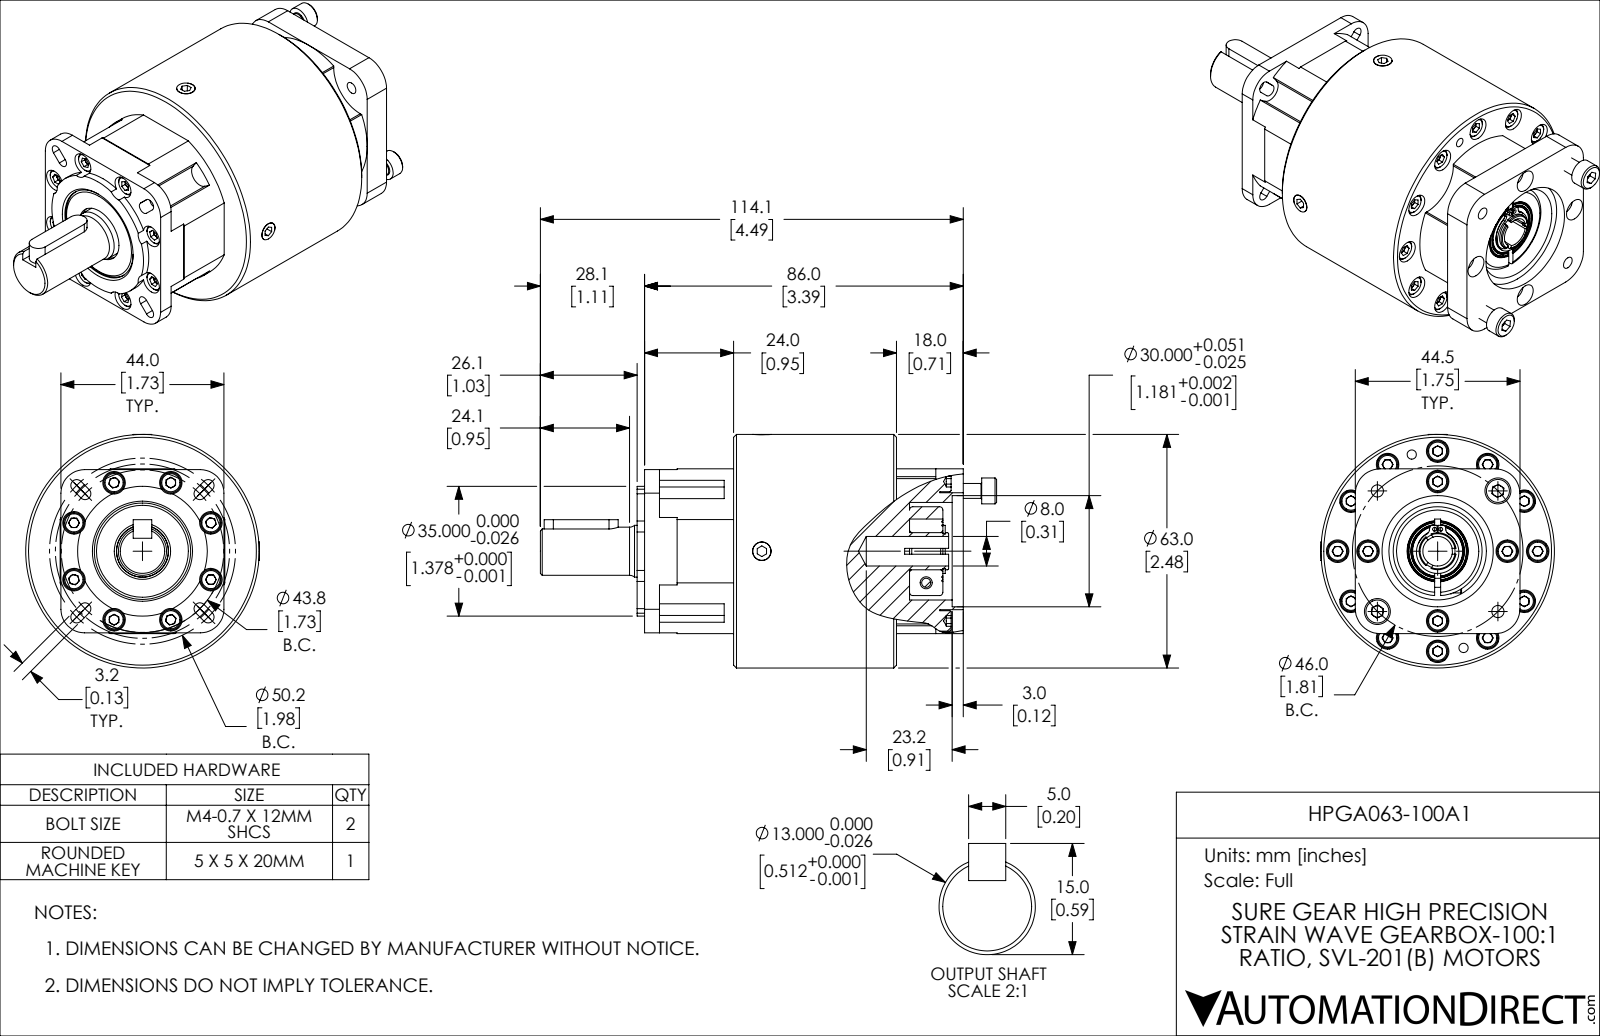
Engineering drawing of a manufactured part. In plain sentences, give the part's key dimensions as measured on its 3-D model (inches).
The part is named "HPGA063-100A1". Its 3-D file was written by "SolidWorks 2021 (CONFIG_CONTROL_DESIGN)". It is 8 solids with 1004 faces: 537 planar, 291 cylindrical and 176 other. Overall it measures 4.847 by 2.48 by 2.48 inches. Its volume is 12.42 cubic inches and its surface area 52.39 square inches. Round holes: 24 of diameter 0.239, 4 of diameter 0.13, 2 of diameter 0.041, 2 of diameter 0.098, 2 of diameter 0.197, 1 of diameter 0.101, 1 of diameter 0.129, 1 of diameter 0.201, 1 of diameter 0.234, 1 of diameter 0.315, 1 of diameter 0.598, 1 of diameter 1.024. Round bosses or shafts: 25 of diameter 0.217, 2 of diameter 0.276, 2 of diameter 0.196, 2 of diameter 0.157, 1 of diameter 2.48, 1 of diameter 0.945, 1 of diameter 0.551, 1 of diameter 0.512. Partial cylindrical surfaces (rounded edges, fillets, slot ends): 8 of radius 0.063, 4 of radius 0.125, 4 of radius 0.25, 4 of radius 0.265, 4 of radius 0.4, 3 of radius 0.5, 2 of radius 0.02, 2 of radius 0.059. The main face-to-face distances are 1.731, 2.439, 0.709, 1.741, 1.75, 0.946, 2.677, 3.386, 1.741, 3.095. The hole center spacings are 1.063, 1.503, 1.841, 2.054, 0.3, 0.65, 1.664, 1.754.
